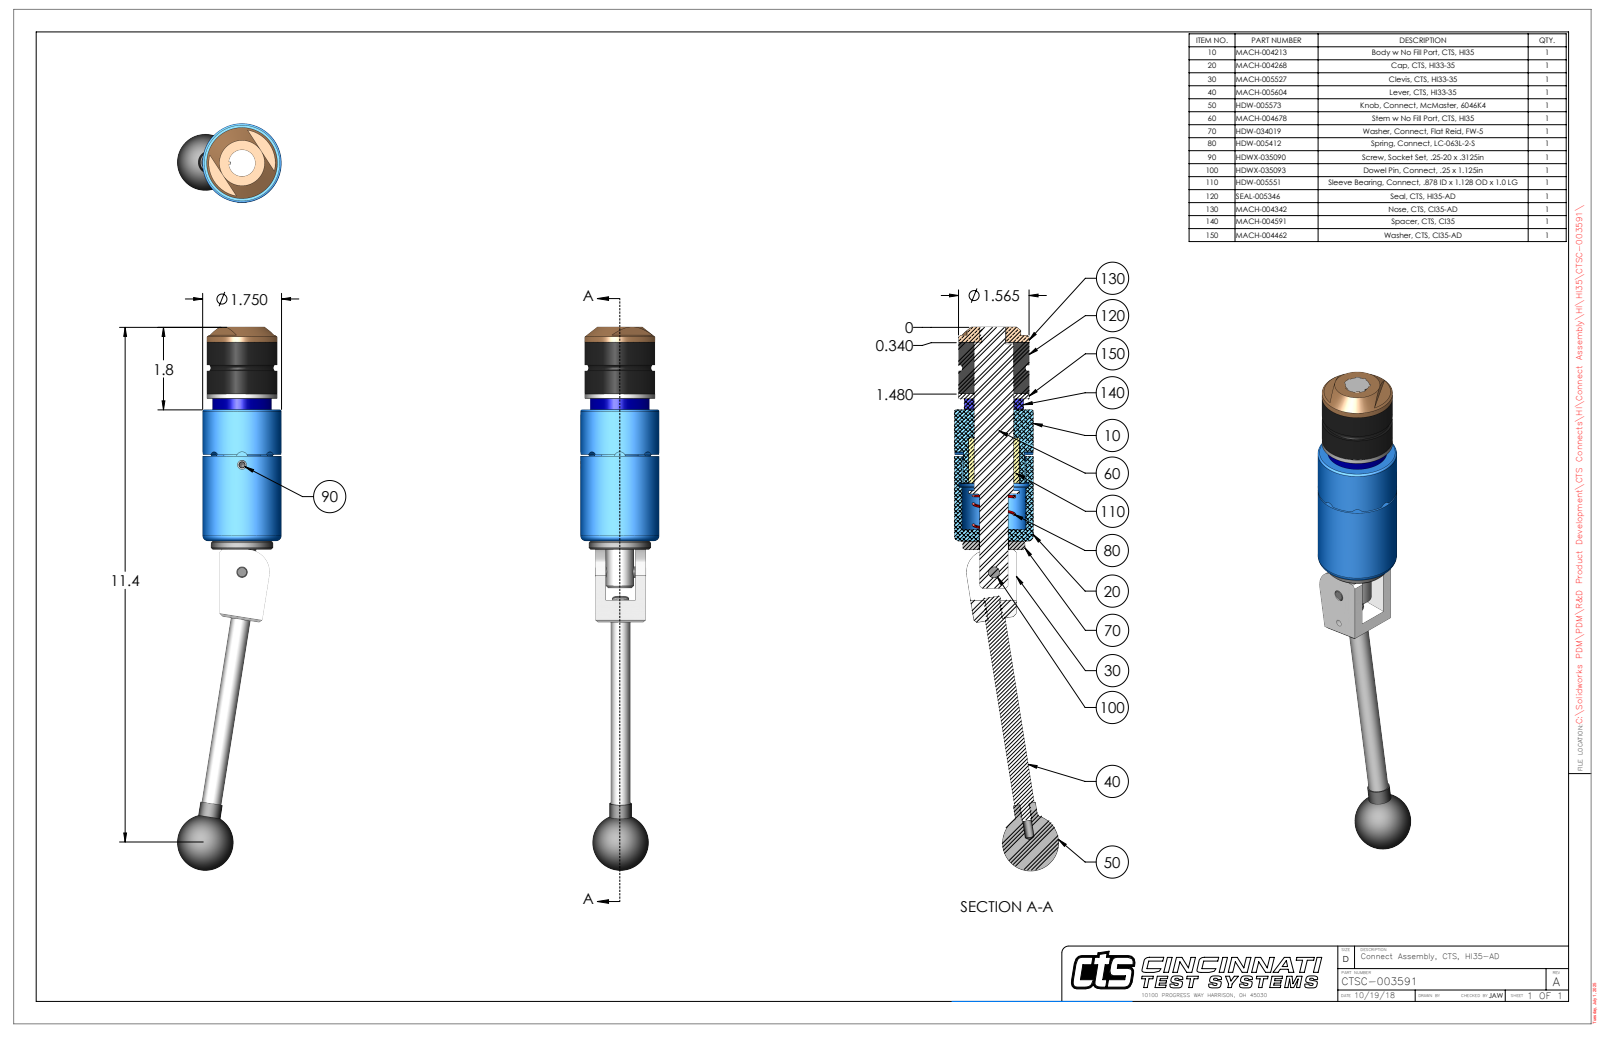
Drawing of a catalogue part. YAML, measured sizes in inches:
part_name: "CTSC-003591"
step_written_by: "SolidWorks 2023 (AUTOMOTIVE_DESIGN)"
units: inches
bodies: {solids: 10, faces: 259, planar: 94, cylindrical: 104, other: 61}
overall_size: [12.039, 2.312, 1.75]
volume: 13.38
surface_area: 79.74
round_holes:
  - {diameter: 0.201, count: 2}
  - {diameter: 0.15, count: 1}
  - {diameter: 0.249, count: 1}
  - {diameter: 0.251, count: 1}
  - {diameter: 0.313, count: 1}
  - {diameter: 0.531, count: 1}
  - {diameter: 0.635, count: 1}
  - {diameter: 0.656, count: 1}
  - {diameter: 0.875, count: 1}
  - {diameter: 0.876, count: 1}
  - {diameter: 0.885, count: 1}
  - {diameter: 1.419, count: 1}
round_bosses_or_shafts:
  - {diameter: 0.25, count: 2}
  - {diameter: 1.75, count: 1}
  - {diameter: 1.565, count: 1}
  - {diameter: 1.565, count: 1}
  - {diameter: 1.38, count: 1}
  - {diameter: 1.312, count: 1}
  - {diameter: 0.871, count: 1}
  - {diameter: 0.869, count: 1}
partial_cylinders:
  - {radius: 0.125, count: 4}
  - {radius: 0.029, count: 2}
  - {radius: 0.5, count: 1}
  - {radius: 0.695, count: 1}
  - {radius: 0.81, count: 1}
face_to_face_distances: [1.14, 4.402, 3.262, 1.49, 0.35, 2.912, 1.25, 0.11, 0.24, 3.152]
hole_center_spacings: [0.74, 2.376, 3.116]
